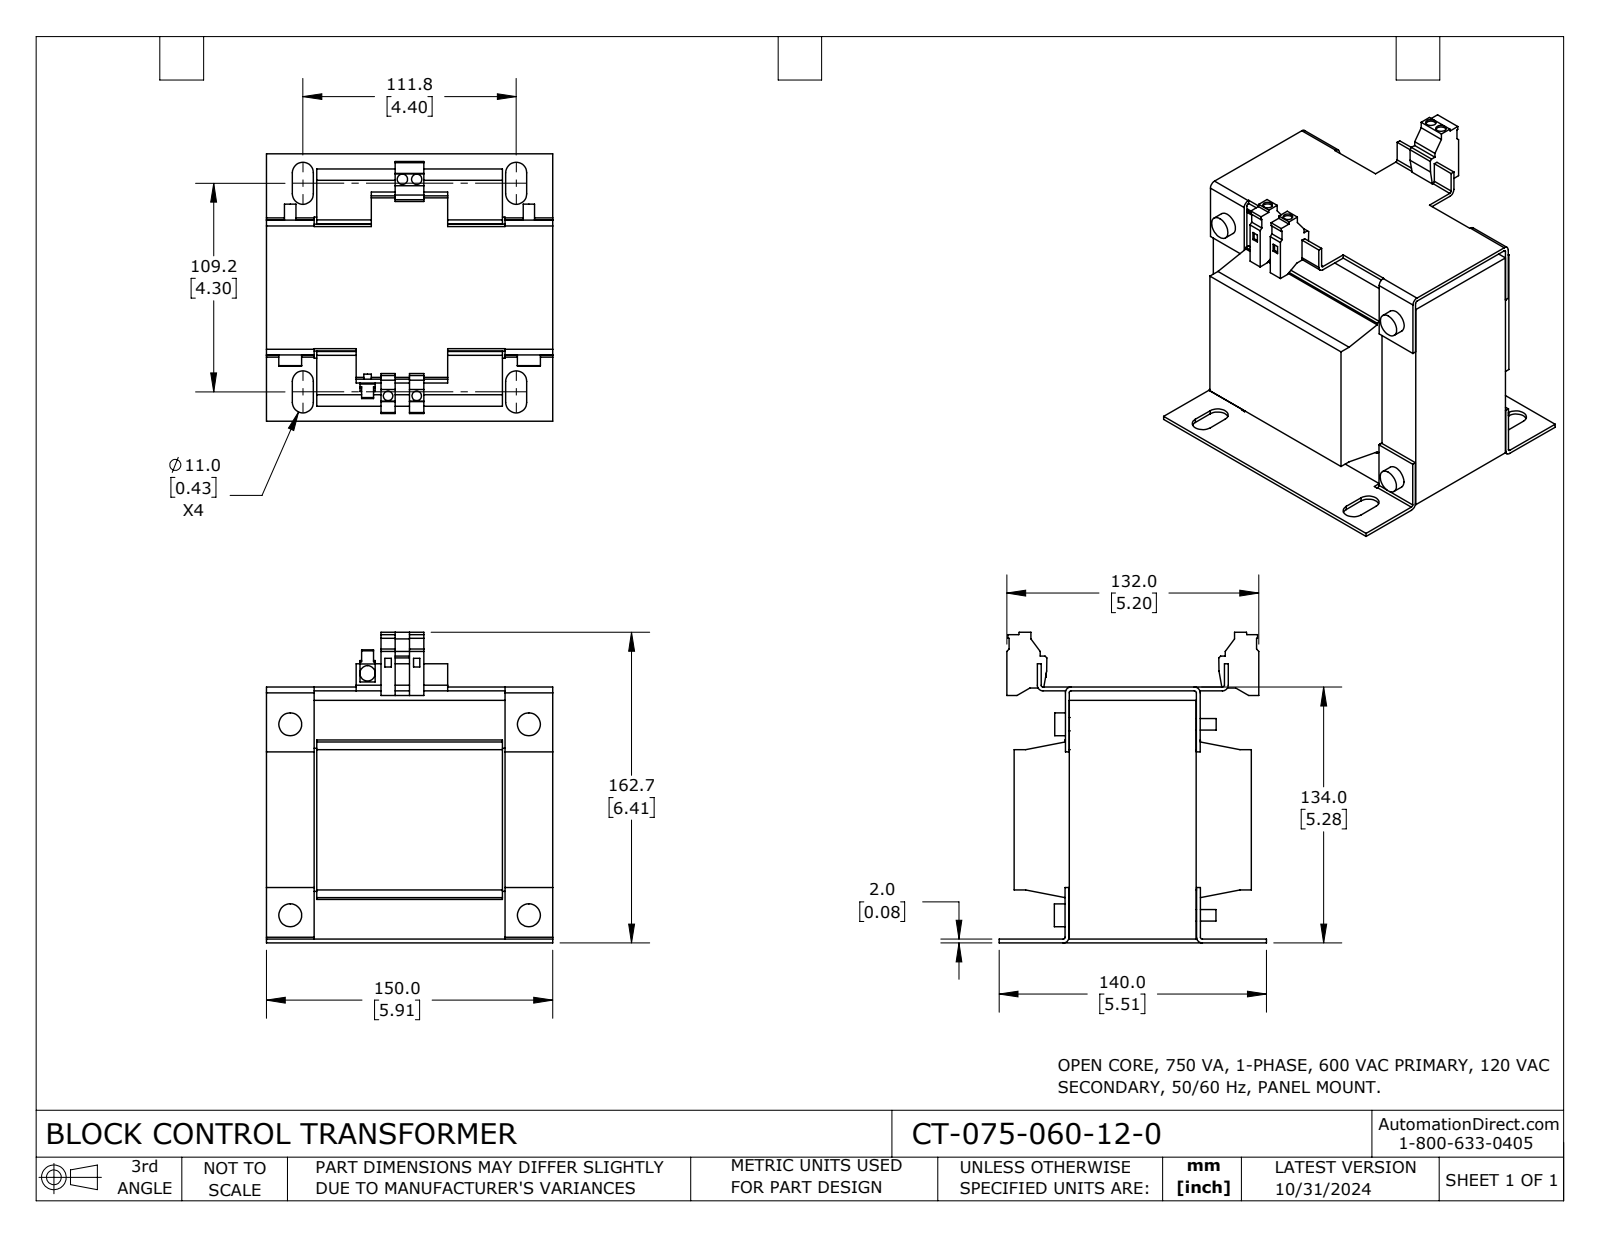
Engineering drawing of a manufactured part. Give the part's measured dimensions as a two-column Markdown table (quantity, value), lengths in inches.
| quantity | value |
| --- | --- |
| part name | CT-075-060-12-0 |
| STEP written by | SolidWorks 2023 (CONFIG_CONTROL_DESIGN) |
| units | inches |
| bodies | 1 solid, 314 faces (233 planar, 81 cylindrical, 0 other) |
| overall size | 6.406 × 5.906 × 5.512 |
| volume | 106.8 in³ |
| surface area | 304.2 in² |
| round holes (diameter × count) | 0.197 × 2, 0.213 × 2 |
| round bosses / shafts (diameter × count) | 0.472 × 4, 0.276 × 4, 0.236 × 4, 0.315 × 1, 0.157 × 1 |
| partial cylindrical surfaces (radius × count) | 0.217 × 8, 0.039 × 6, 0.118 × 6 |
| main face-to-face distances | 0.079, 5.197, 4.921, 1.039, 4.866, 0.984, 1.138, 3.756, 3.937, 2.618 |
| hole center spacings | 4.474, 0.295, 0.591, 4.465, 4.504 |
